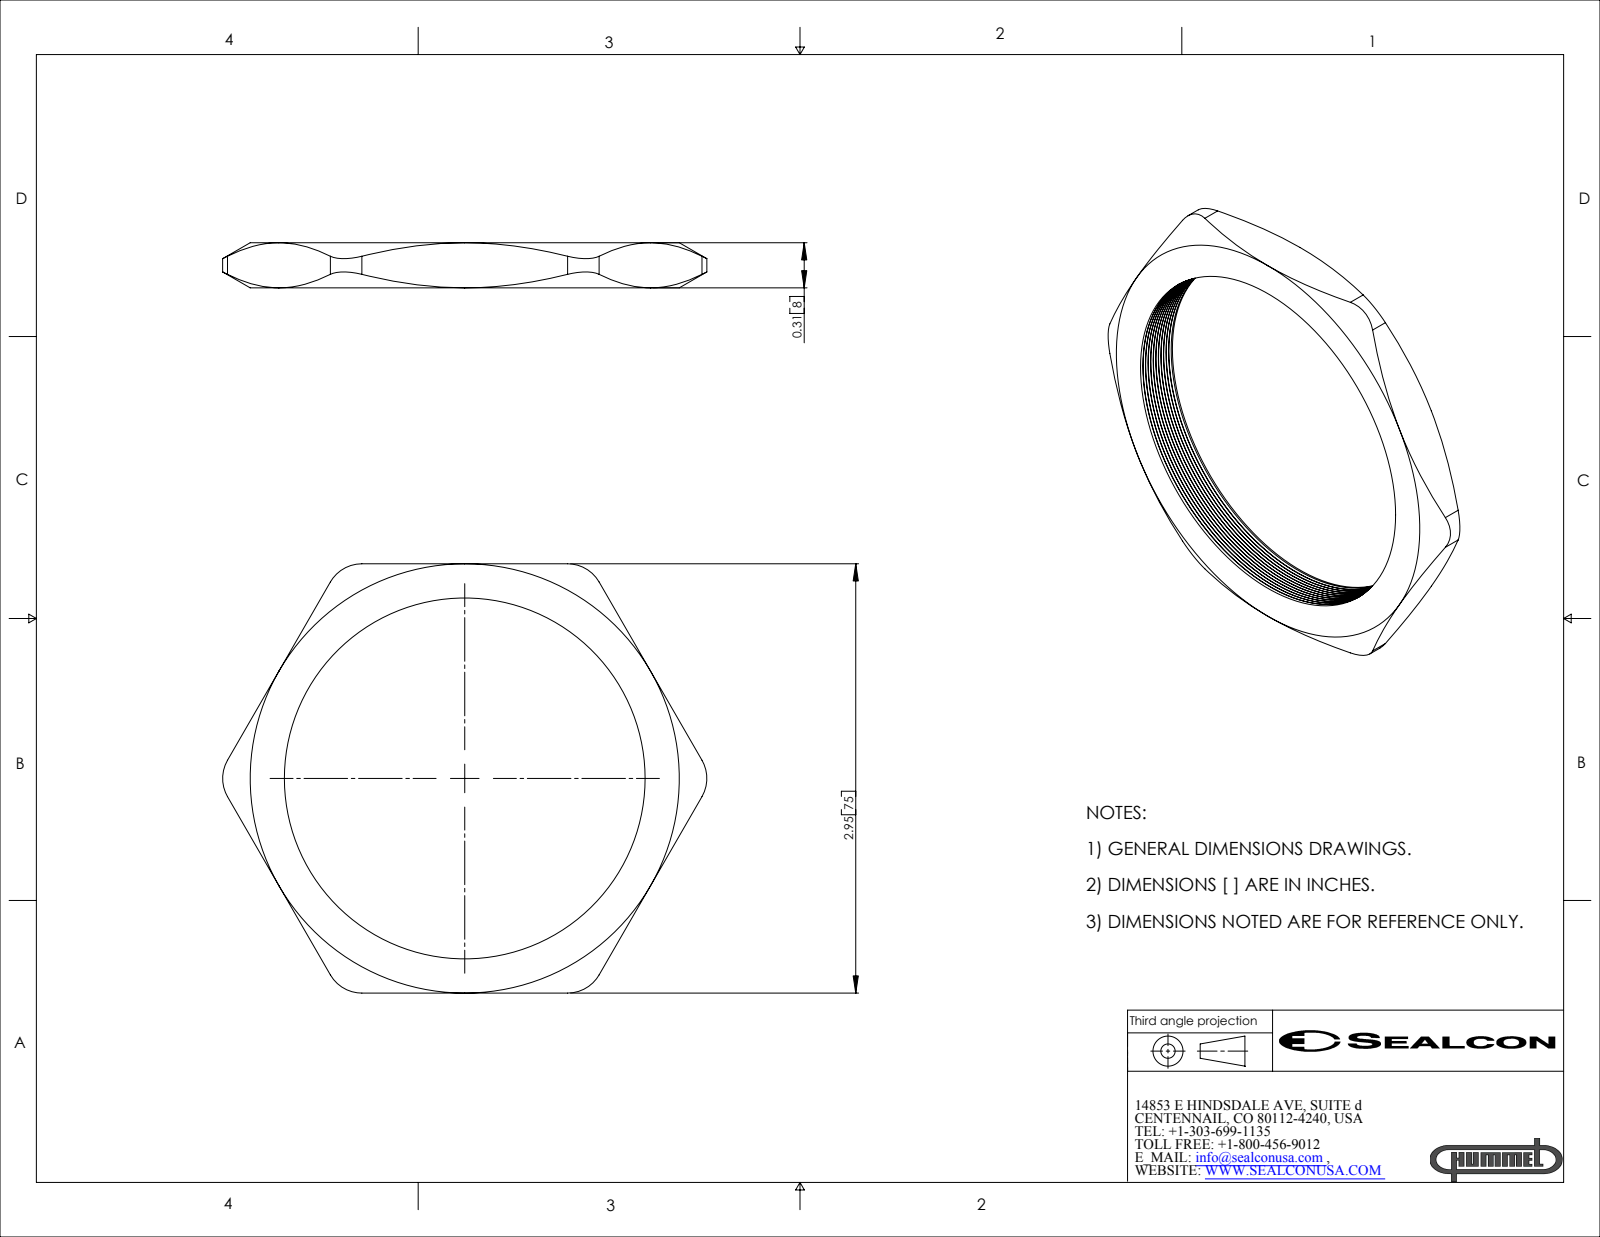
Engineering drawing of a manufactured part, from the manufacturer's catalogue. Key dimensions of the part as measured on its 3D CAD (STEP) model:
Part name (STEP PRODUCT): NM-63-GY
STEP written by: SolidWorks 2007 (CONFIG_CONTROL_DESIGN)
Units: inches
Bodies: 1 solid, 101 faces (8 planar, 31 cylindrical, 62 other)
Overall size (bounding box): 3.329 × 2.95 × 0.31
Volume: 0.76 in³ · Surface area: 12.45 in²
Round holes (diameter × count): ⌀2.48 ×1
Partial cylindrical surfaces — rounded edges, fillets, slot ends (radius × count): R0.25 ×6
Main face-to-face distances: 0.31, 2.95
